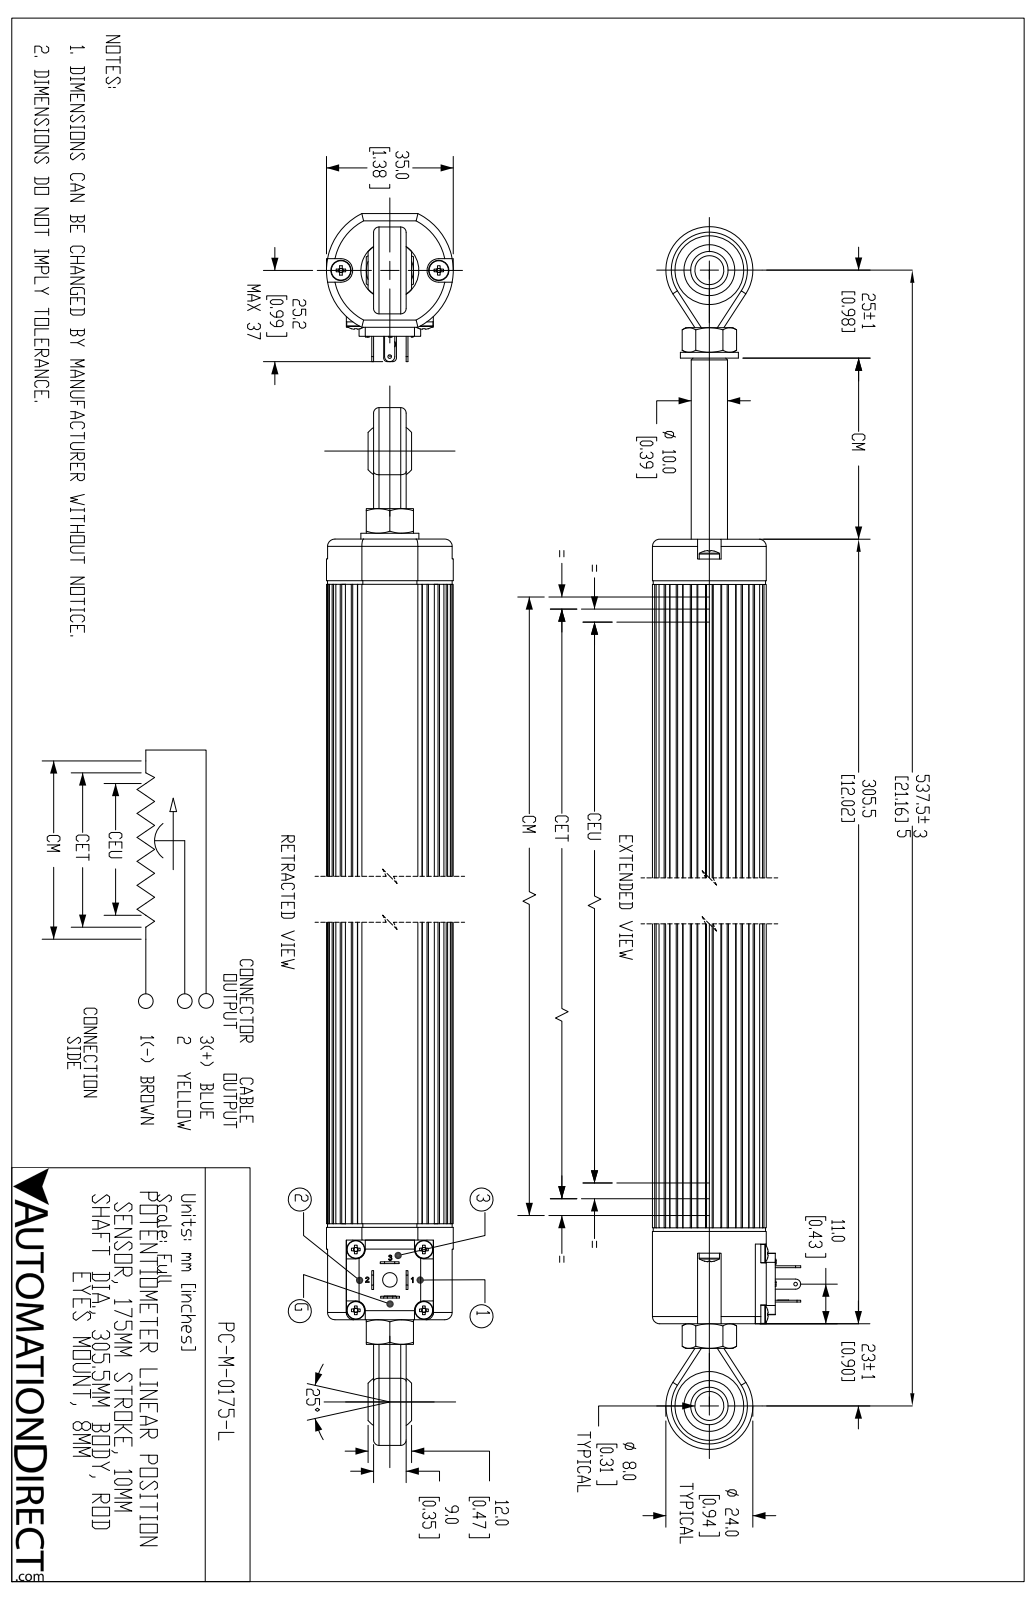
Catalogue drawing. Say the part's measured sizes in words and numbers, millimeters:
The part is named "PC-M-0175-L". Its 3-D file was written by "SolidWorks 2019 (AUTOMOTIVE_DESIGN)". It is 26 solids with 1441 faces: 437 planar, 366 cylindrical and 638 other. Overall it measures 382.6 by 40.9 by 35 millimeters. Its volume is 309 700 cubic millimeters and its surface area 70 000 square millimeters. Round holes: 4 of diameter 2.2, 4 of diameter 2.6, 3 of diameter 1, 2 of diameter 2.7, 2 of diameter 3.5, 2 of diameter 8, 2 of diameter 19, 1 of diameter 2.9, 1 of diameter 4, 1 of diameter 6.8, 1 of diameter 8.4, 1 of diameter 13. Round bosses or shafts: 4 of diameter 5, 4 of diameter 2.5, 3 of diameter 3, 2 of diameter 5.6, 1 of diameter 16, 1 of diameter 10, 1 of diameter 9.9, 1 of diameter 8. Partial cylindrical surfaces (rounded edges, fillets, slot ends): 8 of radius 1.5, 5 of radius 1, 5 of radius 2, 4 of radius 2.6, 4 of radius 3, 2 of radius 1.4, 2 of radius 3.3, 2 of radius 12. The main face-to-face distances are 31.4, 1, 267.5, 266.5, 268.5, 23.2, 3, 28.4, 23.2, 294. The hole center spacings are 12.6, 13.5, 16.8, 18.8, 25.2, 0.6, 2.8, 3.4.
